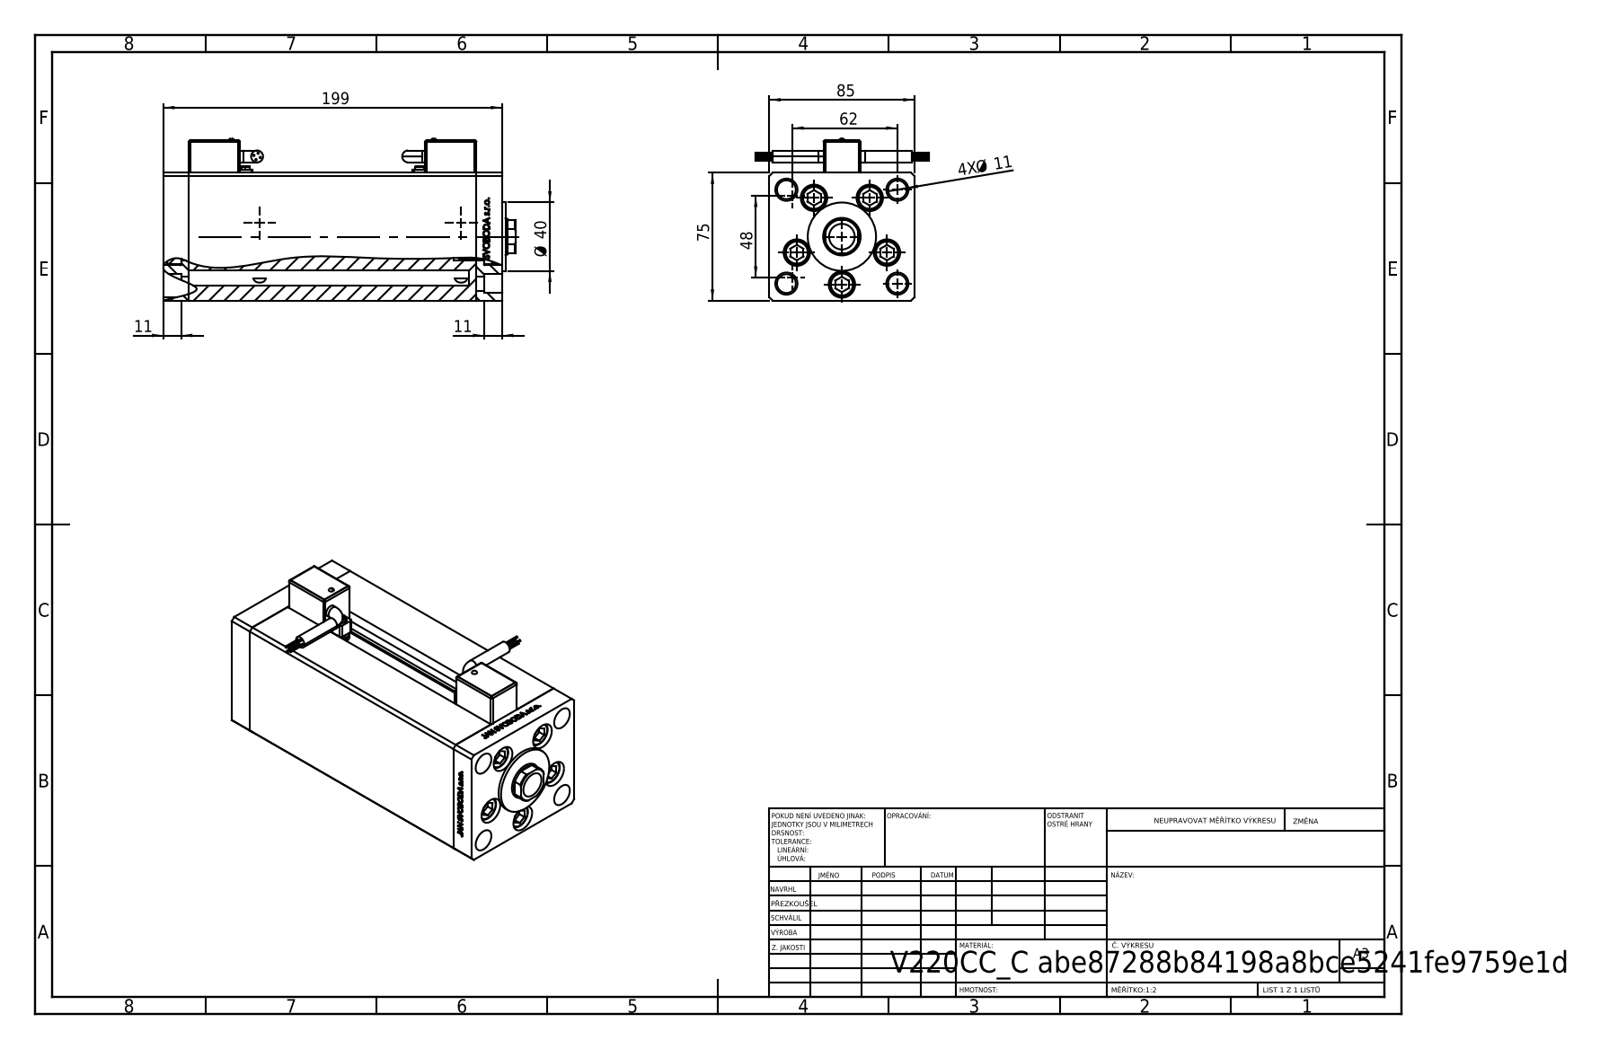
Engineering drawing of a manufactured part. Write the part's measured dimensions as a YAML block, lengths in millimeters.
part_name: "V220C_C MIDDLE; V220C_C CAST PRO VYSUNUTI; ALLEN BOLT; V220C BACK (+2 more)"
step_written_by: "SolidWorks 2019 (CONFIG_CONTROL_DESIGN)"
units: millimeters
bodies: {solids: 16, faces: 1403, planar: 634, cylindrical: 265, other: 504}
overall_size: [206.5, 101.6, 95.1]
volume: 1100000
surface_area: 201324
round_holes:
  - {diameter: 11, count: 9}
  - {diameter: 15.5, count: 5}
  - {diameter: 2, count: 4}
  - {diameter: 9, count: 4}
  - {diameter: 13, count: 4}
  - {diameter: 13.16, count: 4}
  - {diameter: 3.6, count: 2}
  - {diameter: 5, count: 2}
  - {diameter: 7, count: 2}
  - {diameter: 15, count: 1}
  - {diameter: 22, count: 1}
round_bosses_or_shafts:
  - {diameter: 0.85, count: 8}
  - {diameter: 14.5, count: 5}
  - {diameter: 8, count: 5}
  - {diameter: 7, count: 4}
  - {diameter: 6, count: 2}
  - {diameter: 3.5, count: 2}
  - {diameter: 2.5, count: 2}
  - {diameter: 40, count: 1}
partial_cylinders:
  - {radius: 1, count: 24}
  - {radius: 4, count: 4}
  - {radius: 0.93, count: 2}
  - {radius: 10.5, count: 1}
face_to_face_distances: [85, 75, 168.5, 15, 183.5, 10.5, 68.5, 198.5, 6.5, 4.5]
hole_center_spacings: [28, 4.95, 37.64, 42.57, 51.62, 61.6, 80.22, 8.25]
